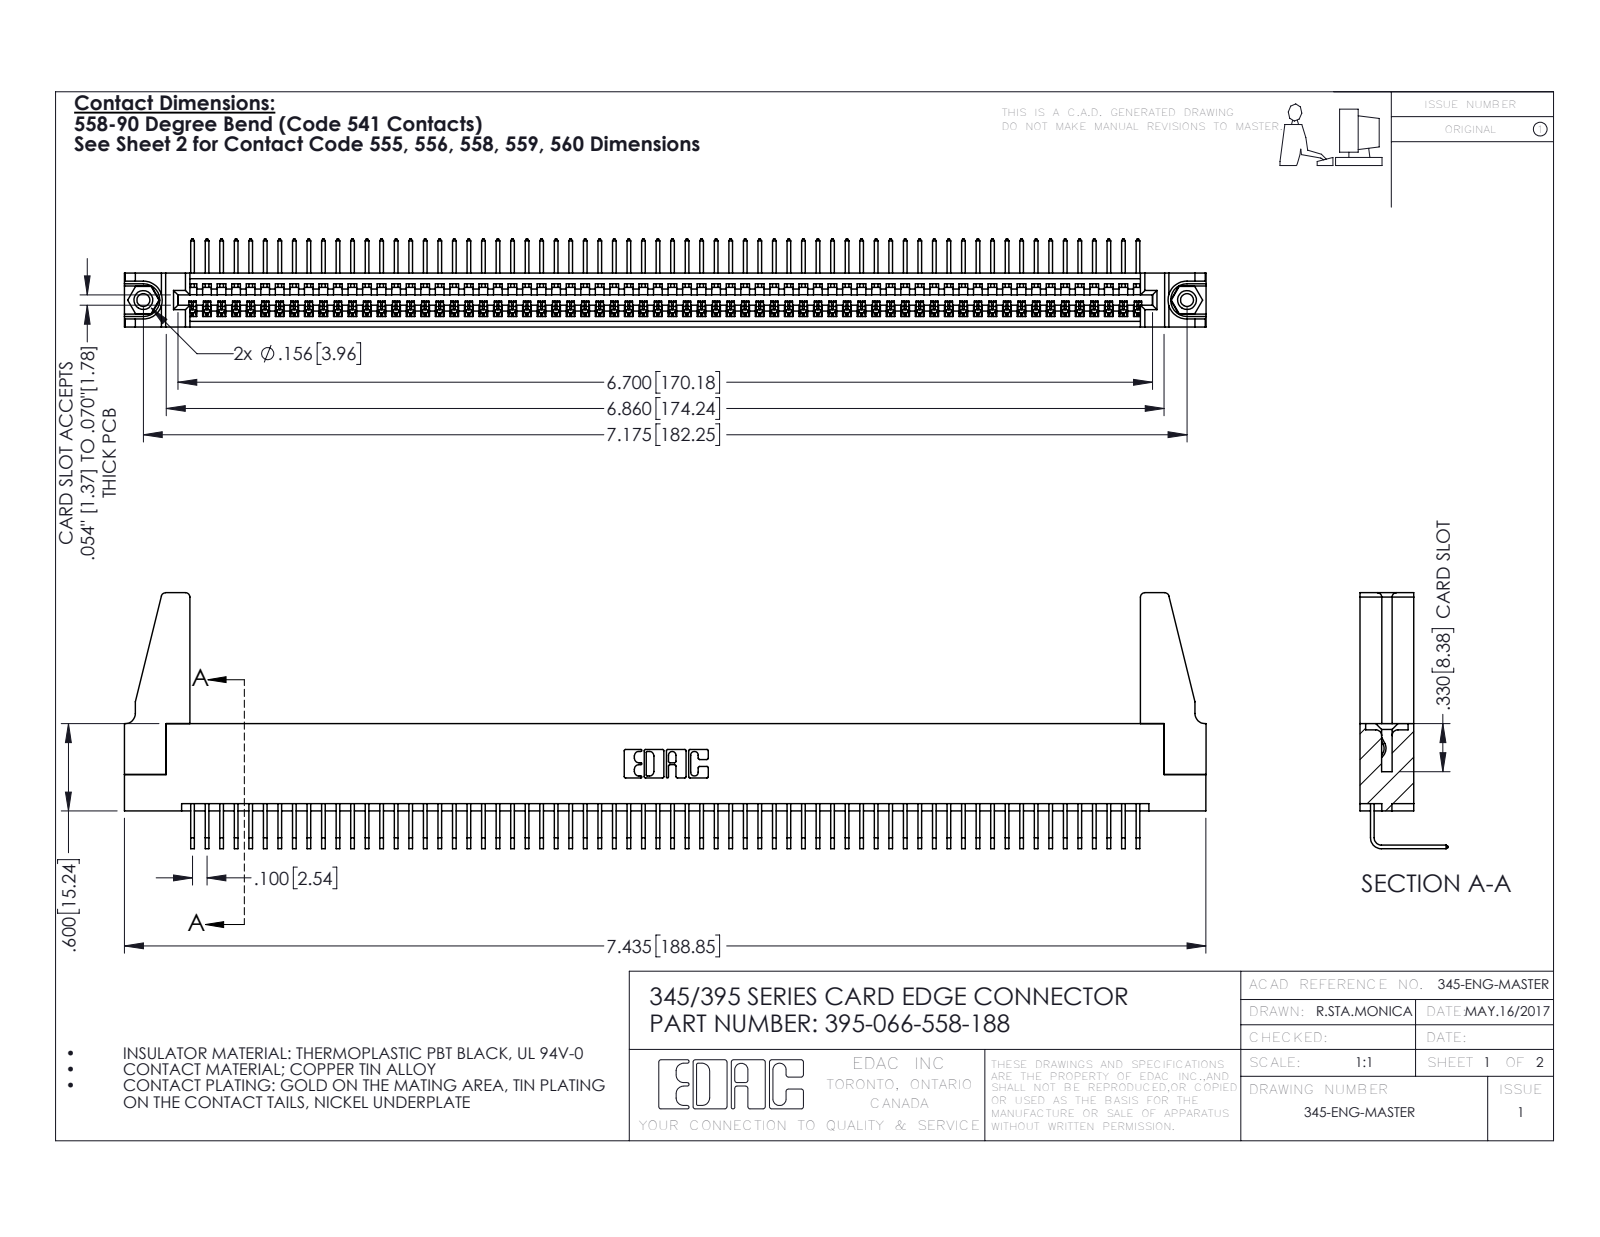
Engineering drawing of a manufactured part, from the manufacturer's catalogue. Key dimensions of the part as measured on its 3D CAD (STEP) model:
Part name (STEP PRODUCT): 345-292-001_558 Tail - 2; 345-250-001_345-250-001-102; 395-066-558-188; 345-220-078_345-220-088 (+1 more)
STEP written by: SolidWorks 2016 (CONFIG_CONTROL_DESIGN)
Units: inches
Bodies: 71 solids, 4210 faces (2924 planar, 1270 cylindrical, 16 other)
Overall size (bounding box): 7.436 × 1.759 × 0.605
Volume: 1.319 in³ · Surface area: 45.17 in²
Round holes (diameter × count): ⌀0.089 ×2, ⌀0.125 ×2, ⌀0.156 ×2, ⌀0.064 ×1
Round bosses / shafts (diameter × count): ⌀0.155 ×2
Partial cylindrical surfaces — rounded edges, fillets, slot ends (radius × count): R0.006 ×132, R0.01 ×22, R0.03 ×8, R0.007 ×6, R0.031 ×6, R0.026 ×3, R0.031 ×2, R0.04 ×2
Main face-to-face distances: 0.072, 0.298, 0.37, 0.2, 0.098, 0.272, 0.025, 0.225, 0.149, 0.072
Hole centre spacings: 0.27, 6.939, 7.175
